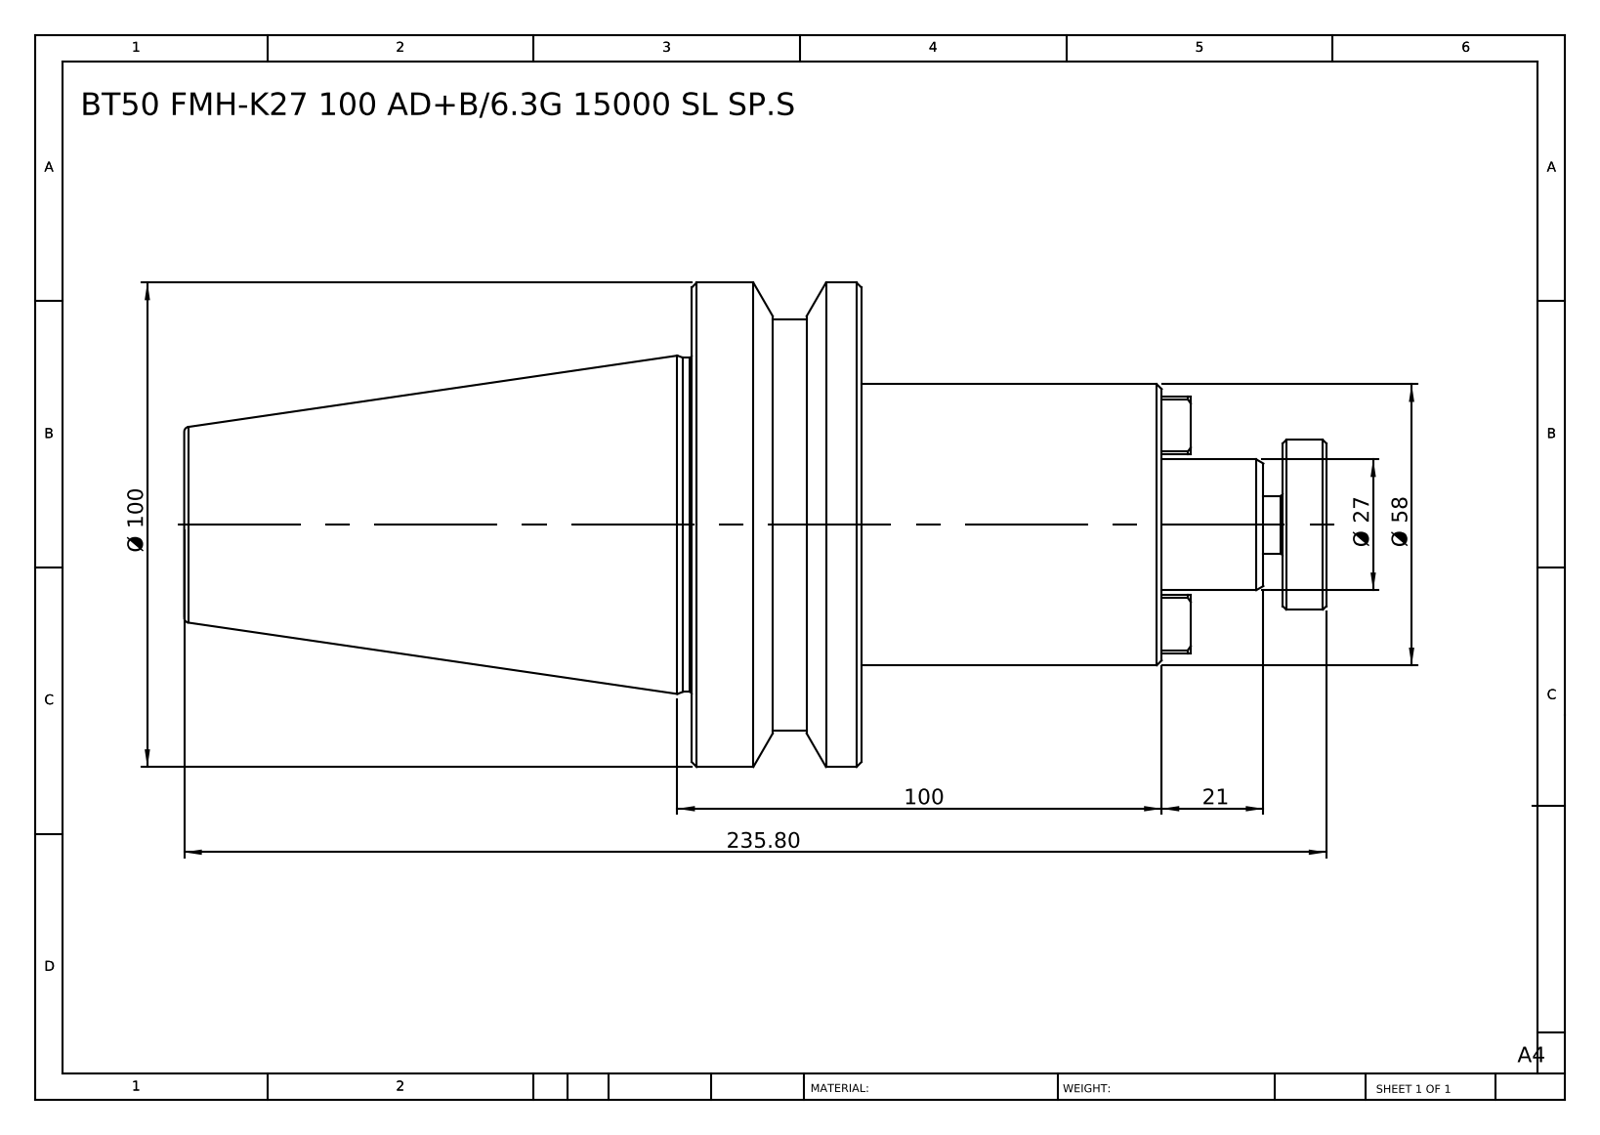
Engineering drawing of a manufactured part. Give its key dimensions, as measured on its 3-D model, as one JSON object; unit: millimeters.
{"part_name": "BT50 FMH27 100 AD-6.3G 15000 SL SP.S", "step_written_by": "SolidWorks 2014 (CONFIG_CONTROL_DESIGN)", "units": "millimeters", "bodies": {"solids": 1, "faces": 77, "planar": 35, "cylindrical": 16, "other": 26}, "overall_size": [235.8, 100, 100], "volume_mm3": 696583, "surface_area_mm2": 60574, "round_bosses_or_shafts": [[100, 1], [85, 1], [69, 1], [58, 1], [35, 1], [27, 1], [12, 1]], "face_to_face_distances": [35, 62, 97, 201.8, 139.8, 104.8, 34, 96, 131, 235.8]}
